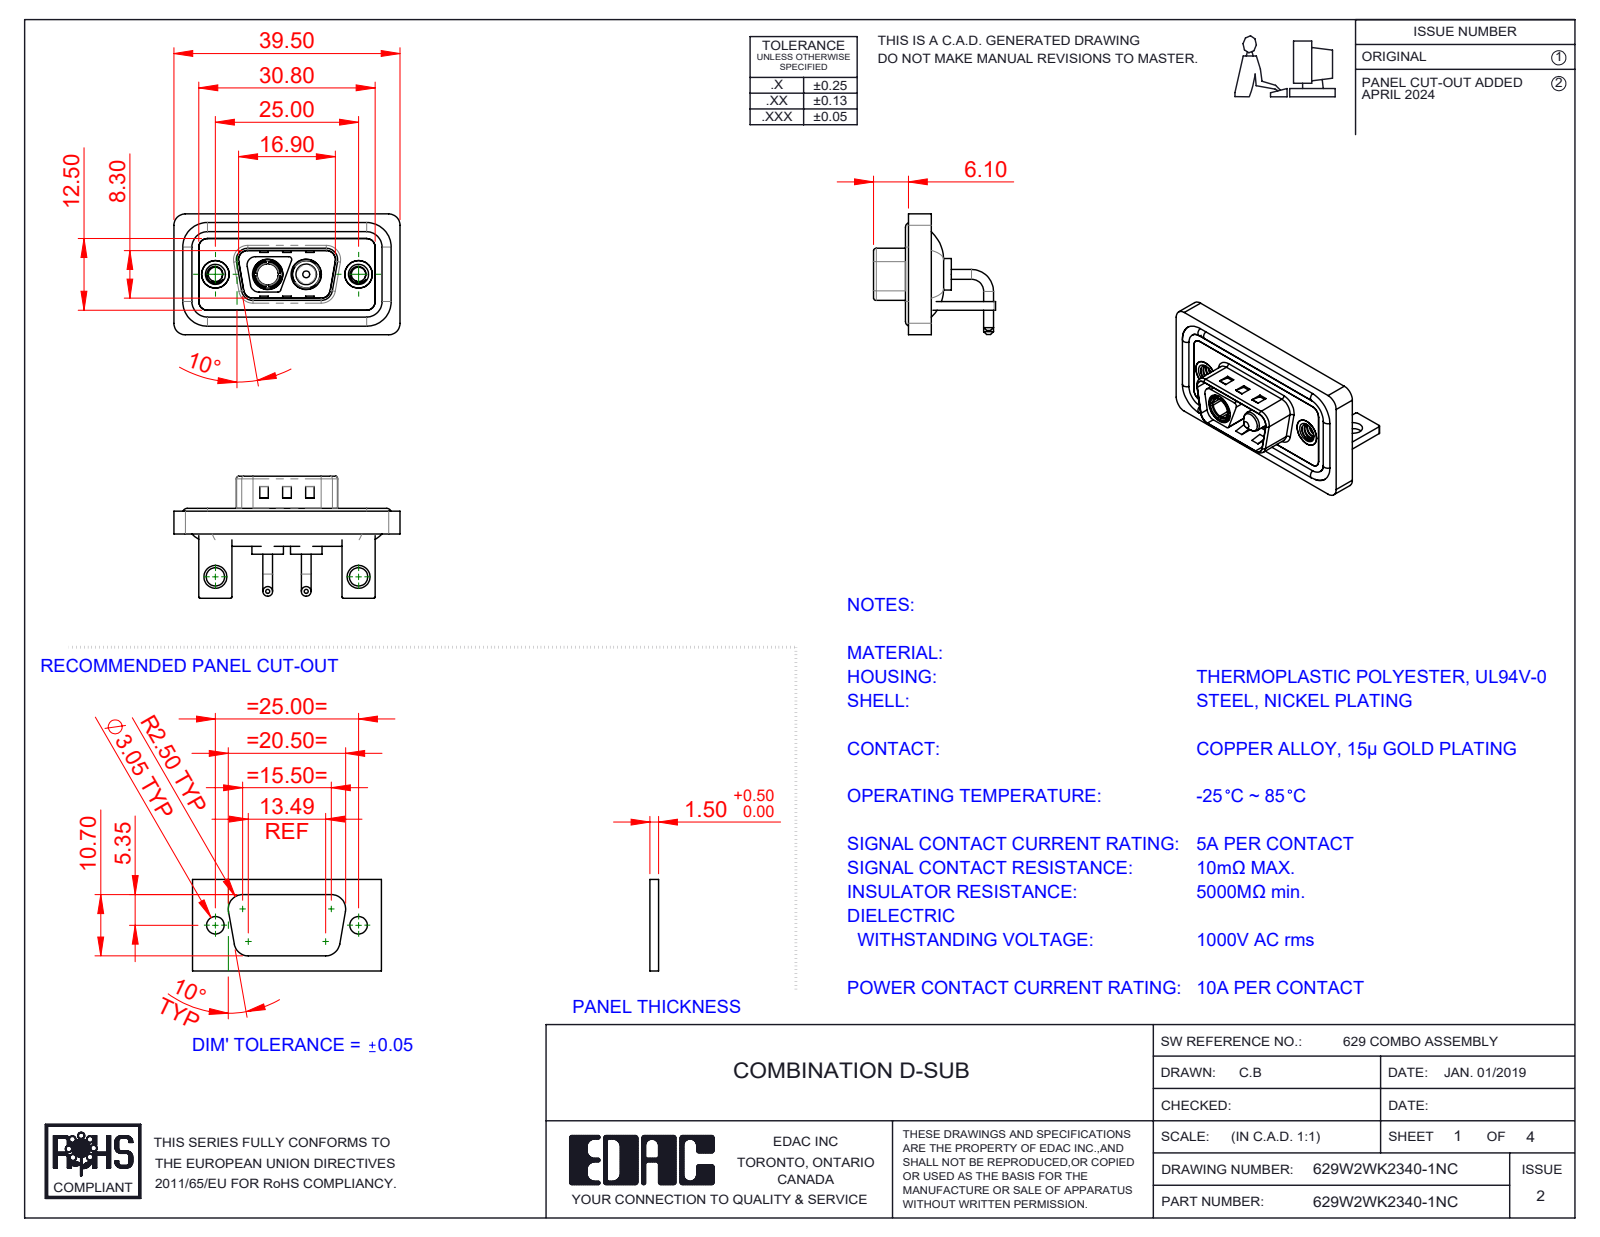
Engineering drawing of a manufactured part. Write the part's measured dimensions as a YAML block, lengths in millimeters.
part_name: "629Combo Housing_2WK2; Power Socket_10A RA; Power Pin_10A RA; 629Combo Stabilizer Bracket (+5 more)"
step_written_by: "SolidWorks 2023 (CONFIG_CONTROL_DESIGN)"
units: millimeters
bodies: {solids: 13, faces: 580, planar: 209, cylindrical: 249, other: 122}
overall_size: [39.5, 21.3, 21.1]
volume: 4836
surface_area: 8016
round_holes:
  - {diameter: 2.5, count: 2}
  - {diameter: 3.2, count: 2}
  - {diameter: 4, count: 2}
  - {diameter: 4.8, count: 2}
  - {diameter: 4.85, count: 2}
  - {diameter: 5, count: 2}
  - {diameter: 5.3, count: 2}
  - {diameter: 3.7, count: 1}
round_bosses_or_shafts:
  - {diameter: 1.7, count: 4}
  - {diameter: 1.6, count: 4}
  - {diameter: 5.5, count: 2}
  - {diameter: 5.2, count: 2}
  - {diameter: 4.9, count: 2}
  - {diameter: 4.75, count: 2}
  - {diameter: 3.75, count: 2}
  - {diameter: 4.96, count: 1}
partial_cylinders:
  - {radius: 1.5, count: 20}
  - {radius: 2, count: 19}
  - {radius: 0.25, count: 16}
  - {radius: 0.5, count: 11}
  - {radius: 1.6, count: 8}
  - {radius: 0.6, count: 4}
  - {radius: 0.65, count: 4}
  - {radius: 0.9, count: 4}
face_to_face_distances: [0.4, 1.5, 2.9, 0.8, 1.1, 1.2, 2.1, 1.6, 3.7, 2.5]
hole_center_spacings: [9.14, 15.86, 25, 6.72]
